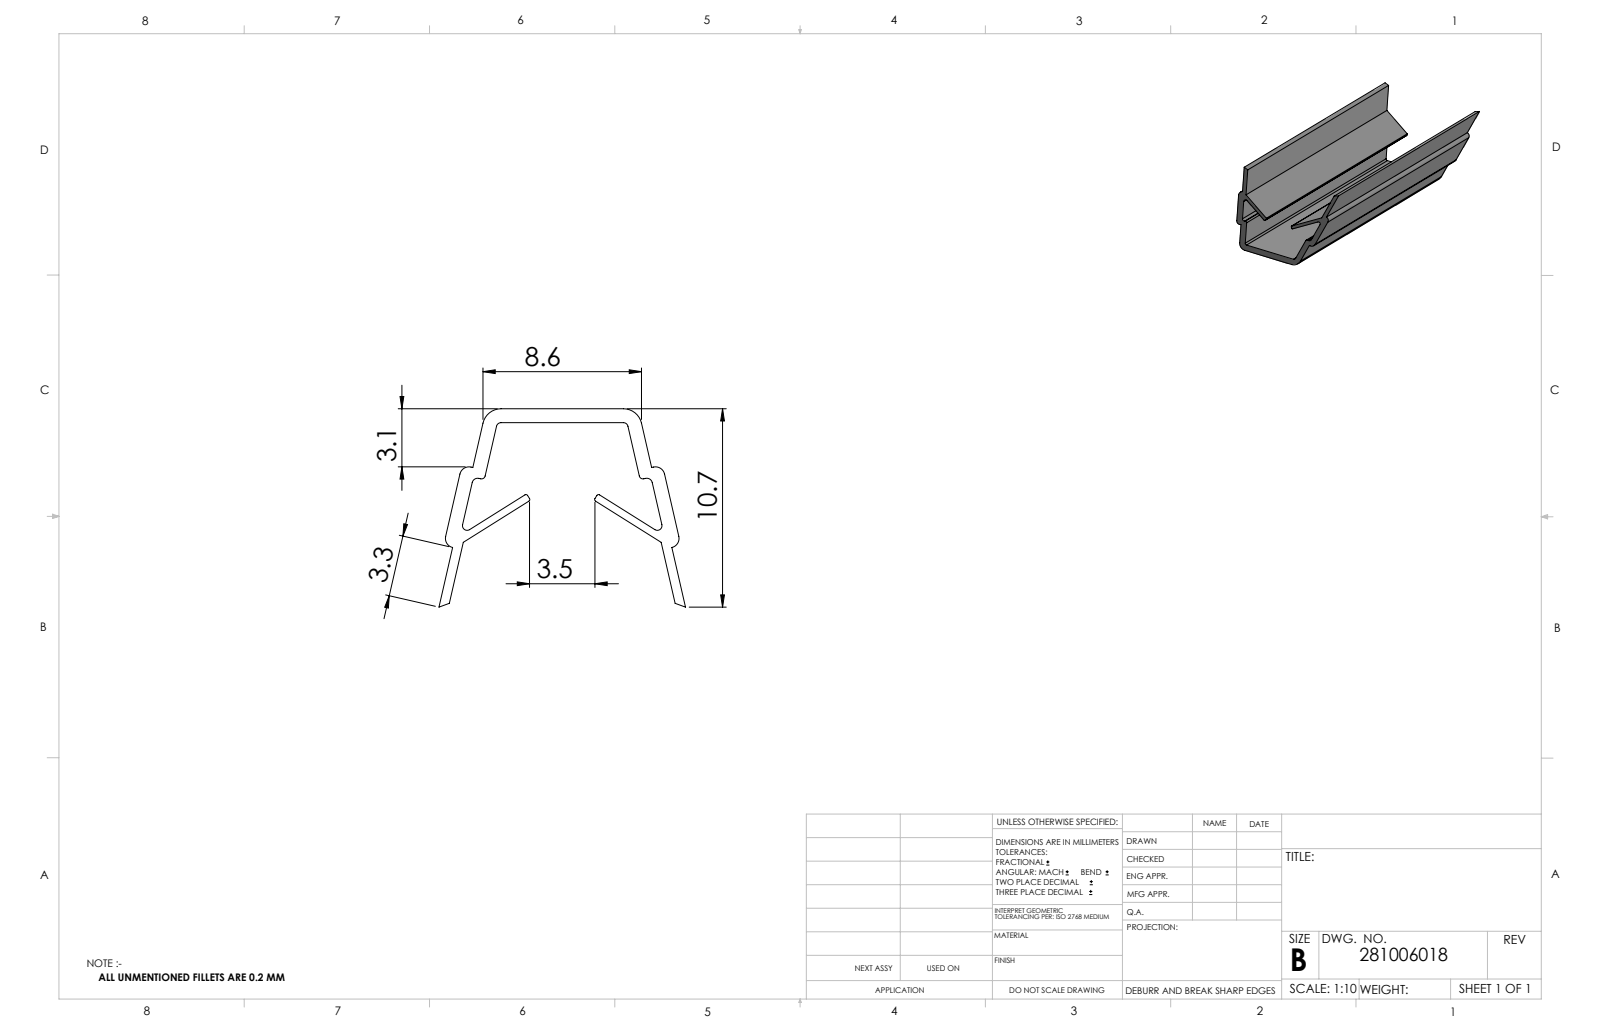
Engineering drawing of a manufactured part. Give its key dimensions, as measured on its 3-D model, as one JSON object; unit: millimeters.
{"part_name": "281006018_c_1", "step_written_by": "SolidWorks 2014 (CONFIG_CONTROL_DESIGN)", "units": "millimeters", "bodies": {"solids": 1, "faces": 49, "planar": 28, "cylindrical": 21, "other": 0}, "overall_size": [1000, 13.31, 10.7], "volume_mm3": 23948, "surface_area_mm2": 75890, "partial_cylinders_radius": [[0.1, 4], [0.25, 4], [0.5, 4], [0.2, 2], [0.3, 2], [1, 2]], "face_to_face_distances": [0.75, 0.5, 0.4, 0.6, 1, 1.35, 0.85, 0.35, 0.51, 1000]}
